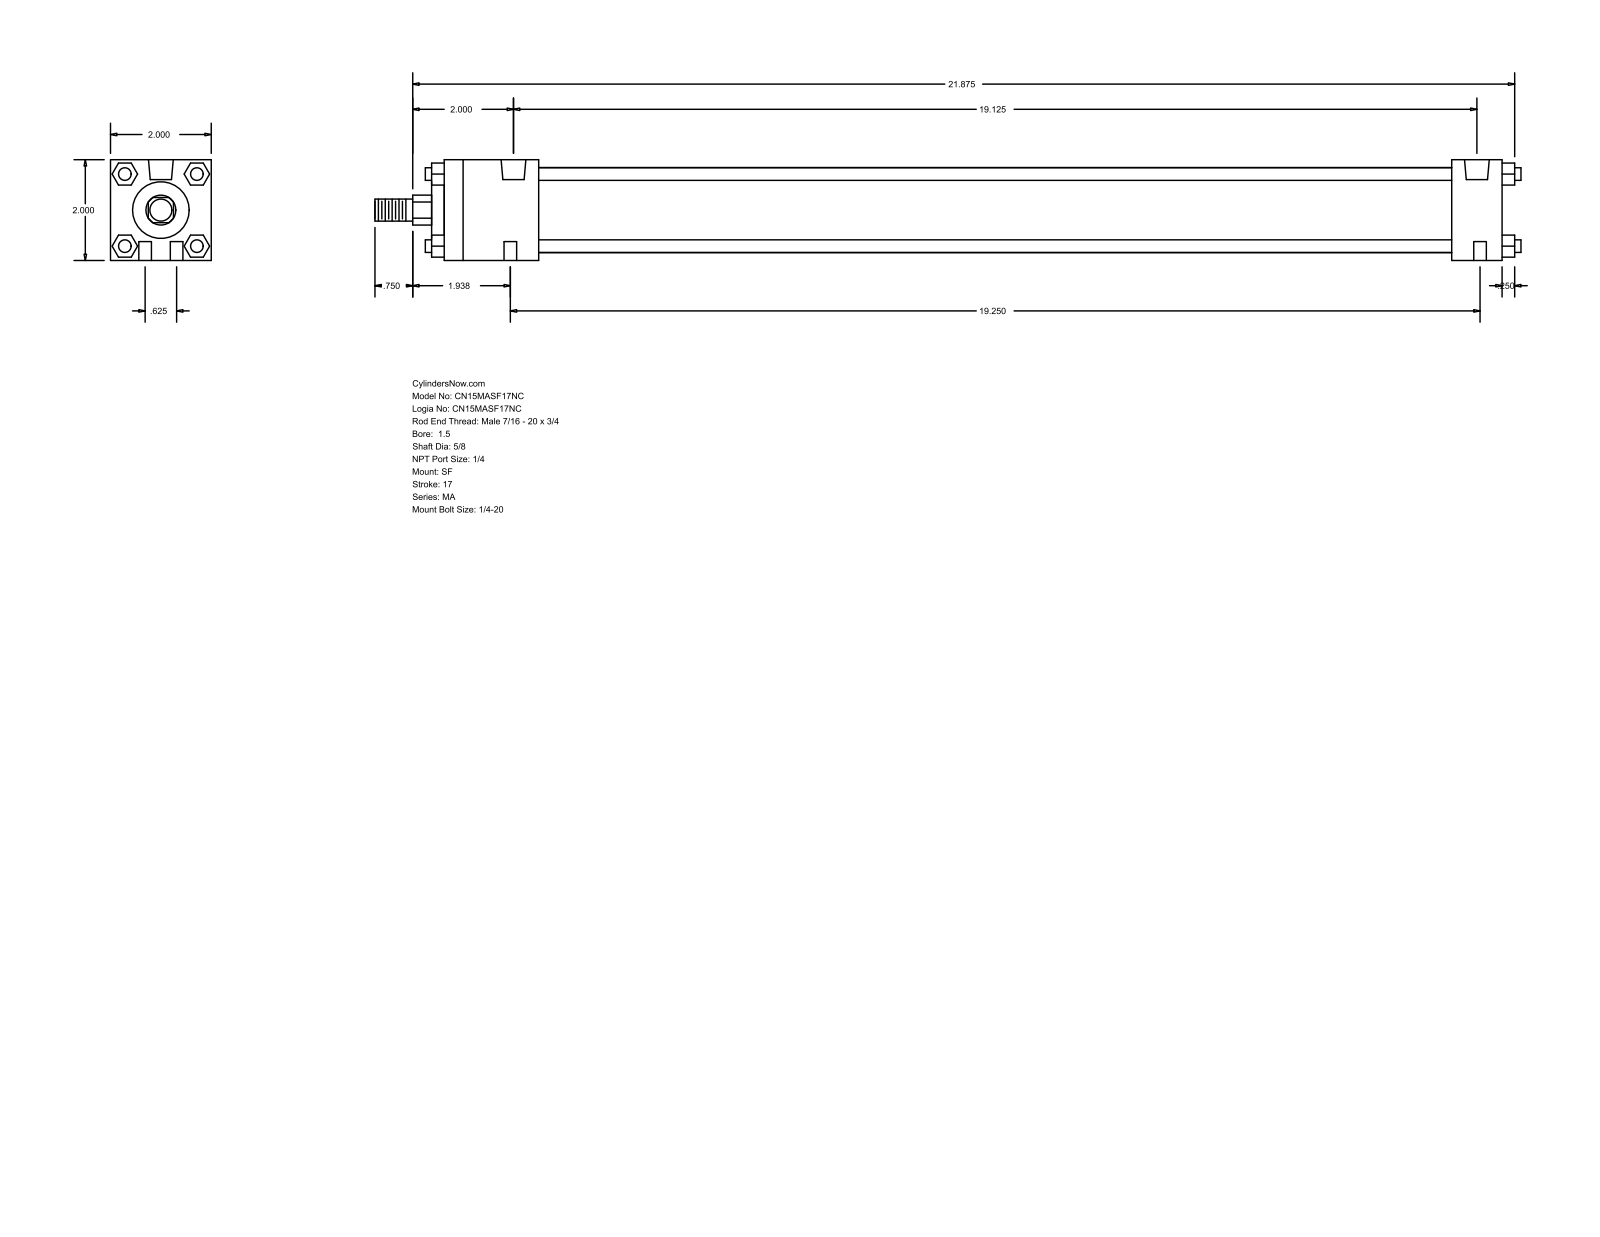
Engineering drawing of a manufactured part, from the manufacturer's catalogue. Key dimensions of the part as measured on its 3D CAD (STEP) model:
Part name (STEP PRODUCT): MA_SF__0150_0.625
STEP written by: GSSL Pune (CONFIG_CONTROL_DESIGN)
Units: millimetres
Bodies: 0 solids, 124 faces (94 planar, 30 cylindrical, 0 other)
Overall size (bounding box): 577.85 × 50.8 × 50.8
Round holes (diameter × count): ⌀6.35 ×4, ⌀7.94 ×2, ⌀12.49 ×2
Round bosses / shafts (diameter × count): ⌀6.35 ×4, ⌀42.93 ×1, ⌀28.57 ×1, ⌀15.88 ×1, ⌀11.11 ×1
Partial cylindrical surfaces — rounded edges, fillets, slot ends (radius × count): R7.54 ×1
Main face-to-face distances: 50.8, 533.39, 6.35, 539.74, 47.62, 508, 460.38, 485.77, 25.39, 53.97
Hole centre spacings: 8.1, 15.88, 485.78, 487.42, 487.43, 488.95, 489.21
